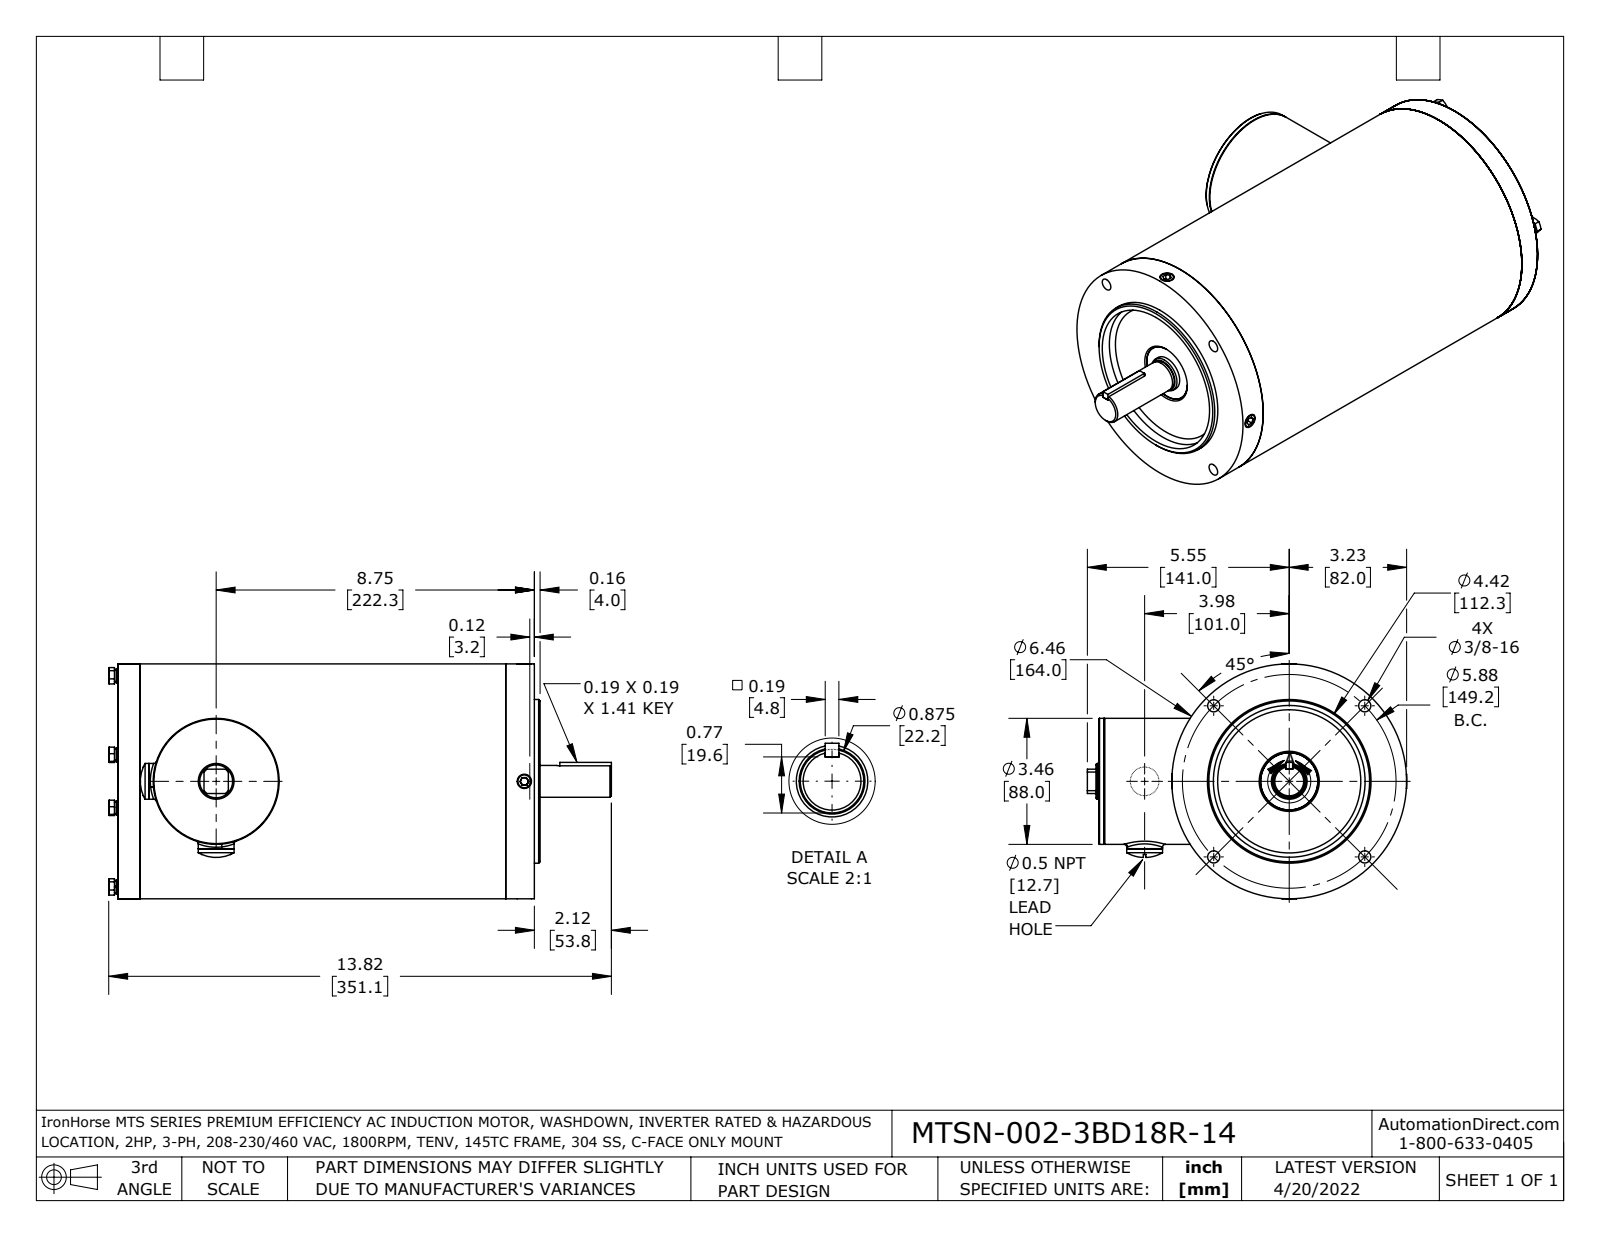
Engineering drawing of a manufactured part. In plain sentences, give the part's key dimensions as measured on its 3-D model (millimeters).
The part is named "(MTSN-002-3BD18R-14) nc WITH -bolts redcmb1 coord fxt". Its 3-D file was written by "SolidWorks 2021 (AUTOMOTIVE_DESIGN)". It is 6 solids with 606 faces: 222 planar, 217 cylindrical and 167 other. Overall it measures 351.1 by 223.4 by 164.3 millimeters. Its volume is 857 400 cubic millimeters and its surface area 495 000 square millimeters. Round holes: 6 of diameter 4.2, 4 of diameter 8.5, 2 of diameter 3, 2 of diameter 16.7, 1 of diameter 26, 1 of diameter 35, 1 of diameter 42, 1 of diameter 52, 1 of diameter 66, 1 of diameter 78, 1 of diameter 82, 1 of diameter 106. Round bosses or shafts: 8 of diameter 10, 5 of diameter 25, 4 of diameter 8, 4 of diameter 6, 2 of diameter 88, 2 of diameter 20, 2 of diameter 17.6, 1 of diameter 164. Partial cylindrical surfaces (rounded edges, fillets, slot ends): 16 of radius 2, 4 of radius 4.5, 4 of radius 5.5, 4 of radius 8, 4 of radius 10, 1 of radius 2.4. The main face-to-face distances are 3, 288, 6, 285, 282, 291, 9, 279, 4, 11. The hole center spacings are 30, 56.7, 74.6, 74.6, 82.1, 87.9, 99.8, 105.5.
